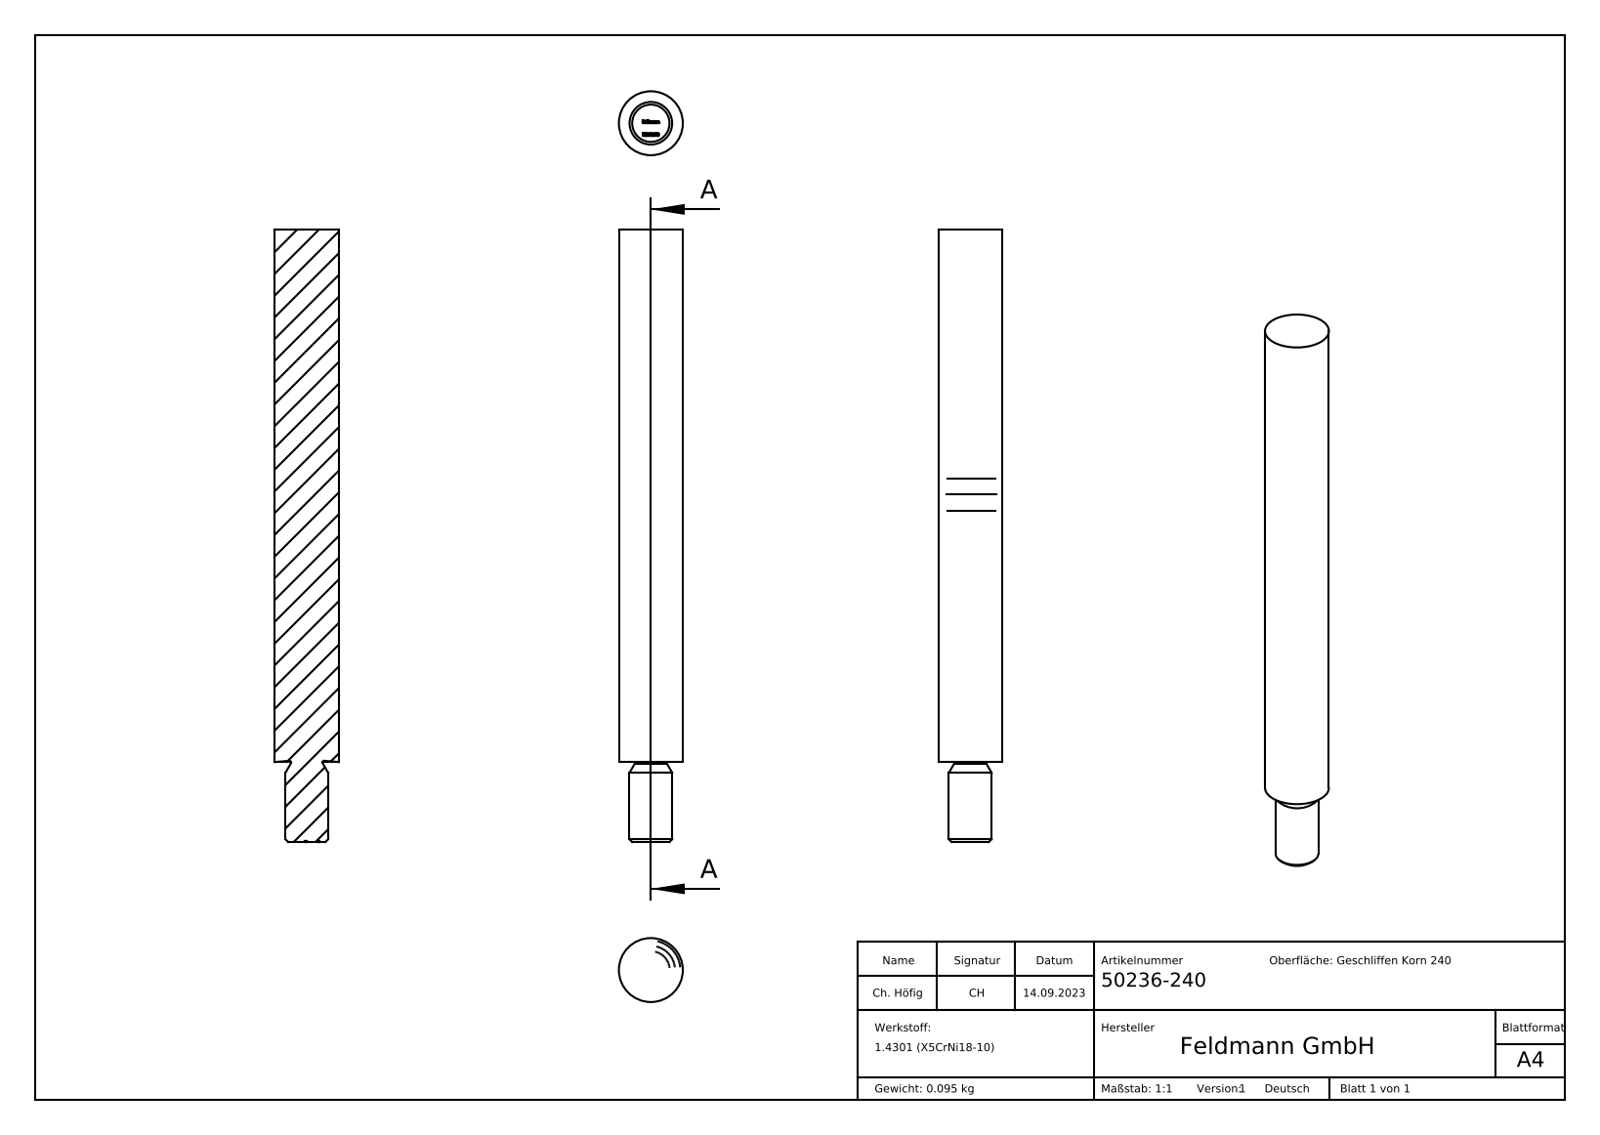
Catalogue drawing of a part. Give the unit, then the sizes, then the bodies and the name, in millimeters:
Units: millimetres
Overall size (bounding box): 115 × 12 × 12
Round bosses / shafts (diameter × count): ⌀12 ×1, ⌀8 ×1
Main face-to-face distances: 115, 114.9, 0.77, 1.29, 2.38, 2.39, 0.72, 1.55, 2.44, 0.57
Volume: 12 025 mm³ · Surface area: 4 394 mm²
Bodies: 1 solid, 266 faces (157 planar, 2 cylindrical, 107 other)
Part name (STEP PRODUCT): 50236-240
STEP written by: SolidWorks 2018 (CONFIG_CONTROL_DESIGN)
